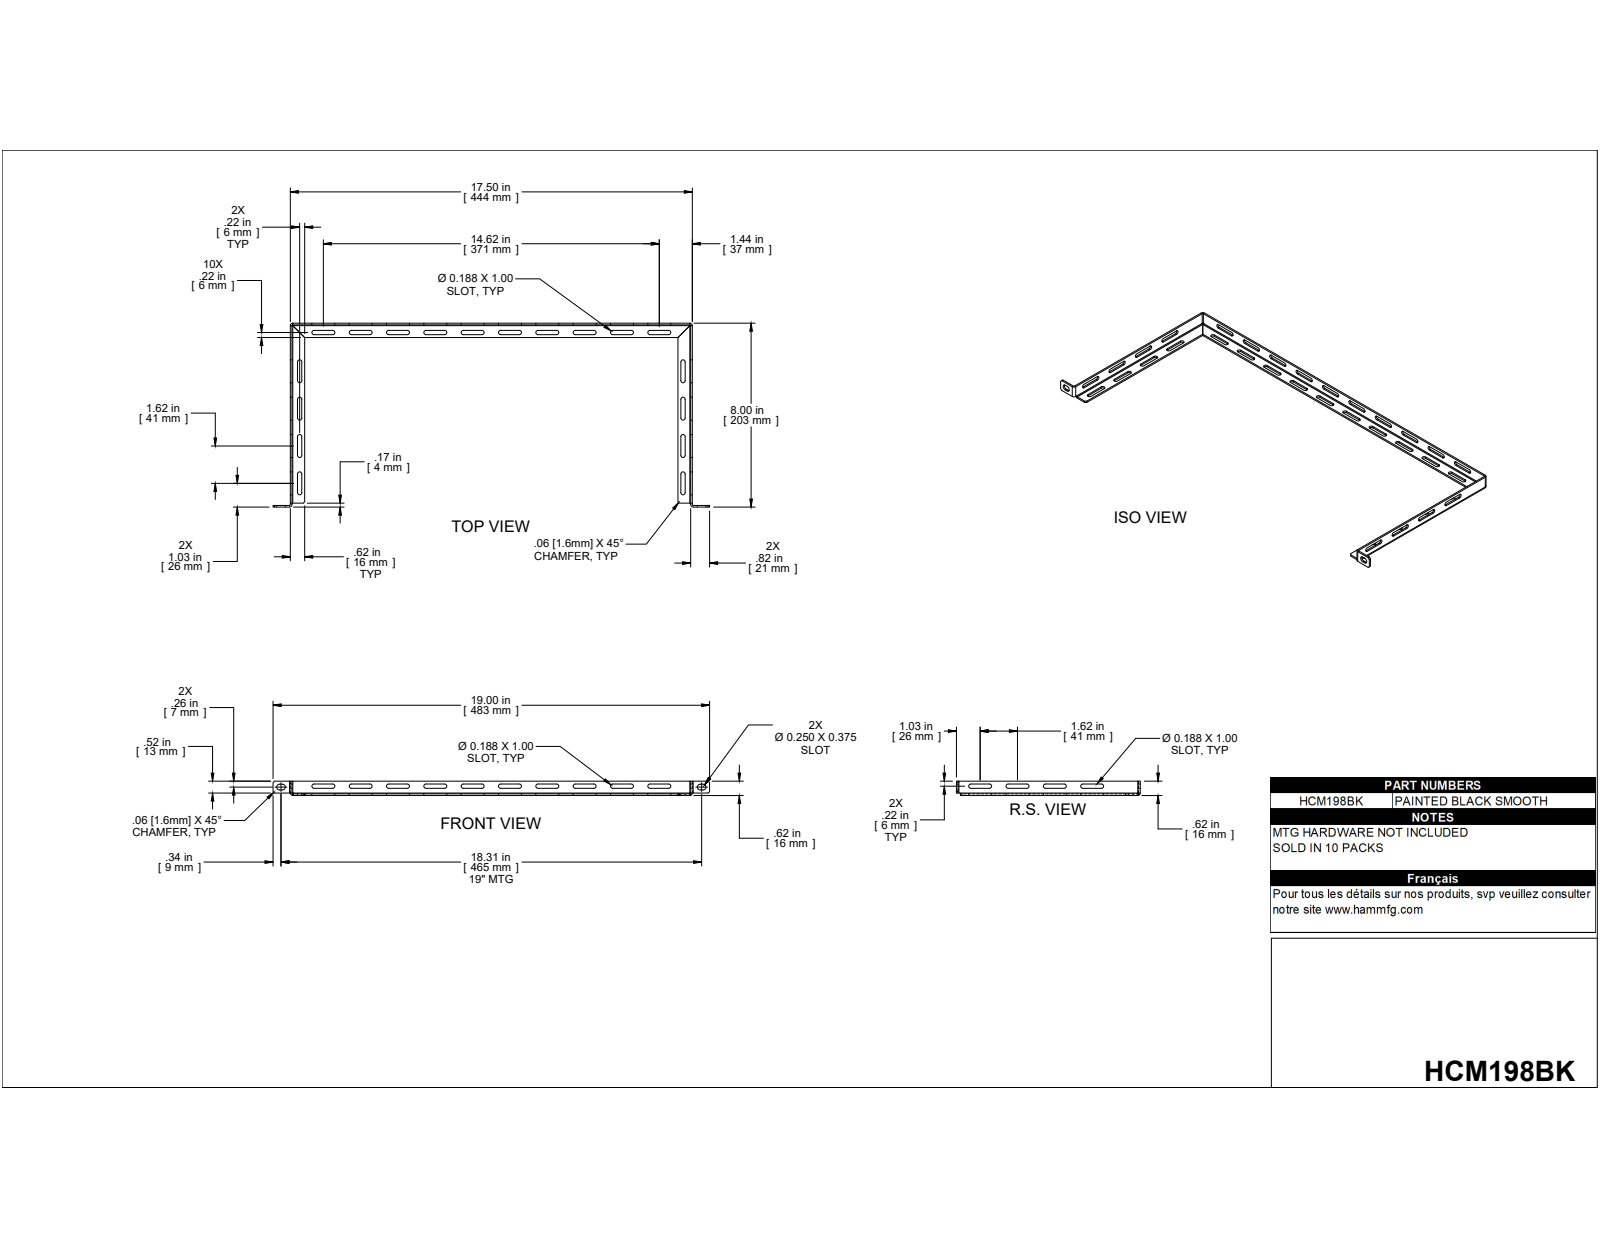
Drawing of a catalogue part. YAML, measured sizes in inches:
part_name: "COM57141-8"
step_written_by: "ST-DEVELOPER v16.7 (AUTOMOTIVE_DESIGN)"
units: inches
bodies: {solids: 1, faces: 212, planar: 118, cylindrical: 90, other: 4}
overall_size: [19, 8, 0.625]
volume: 2.26
surface_area: 73.91
partial_cylinders:
  - {radius: 0.094, count: 65}
  - {radius: 0.036, count: 7}
  - {radius: 0.108, count: 7}
  - {radius: 0.125, count: 4}
face_to_face_distances: [0.072, 17.428, 0.553, 0.625, 17.356, 17.5, 0.313, 0.428, 0.5, 0.241]
